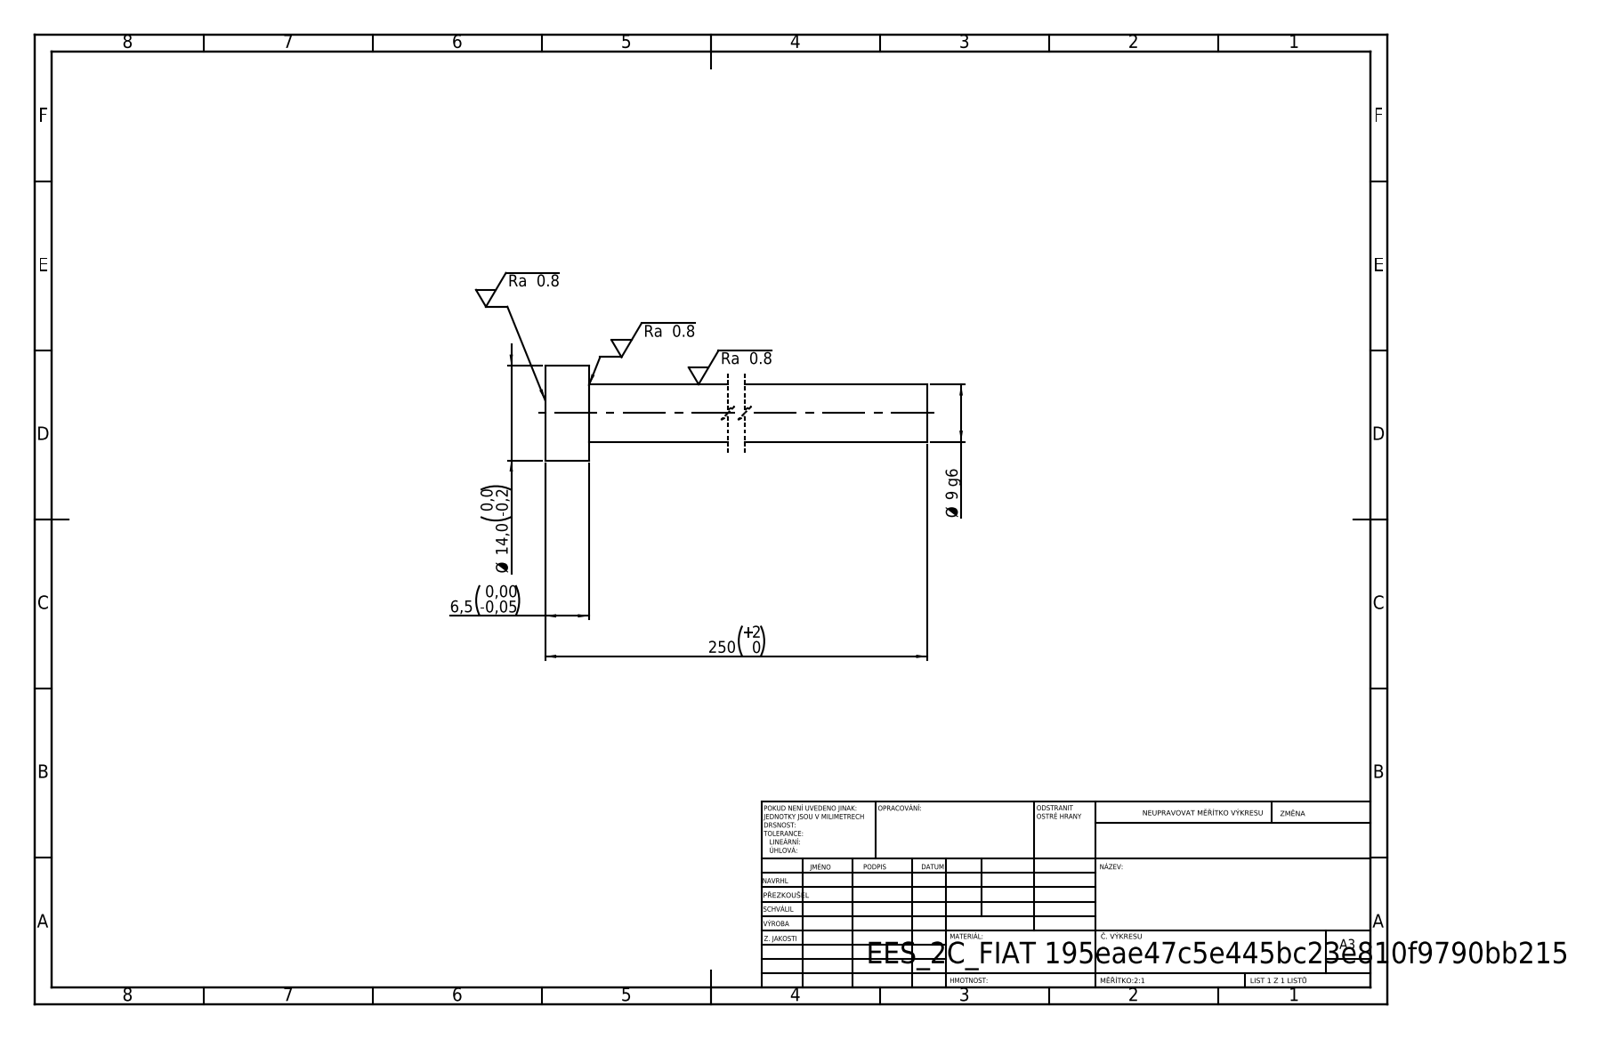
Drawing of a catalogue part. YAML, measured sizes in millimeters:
step_written_by: "SolidWorks 2019 (CONFIG_CONTROL_DESIGN)"
units: millimeters
bodies: {solids: 1, faces: 7, planar: 3, cylindrical: 4, other: 0}
overall_size: [250, 14, 14]
volume: 14818
surface_area: 7096
round_bosses_or_shafts:
  - {diameter: 14, count: 1}
  - {diameter: 8.5, count: 1}
face_to_face_distances: [6.5, 250, 243.5]
